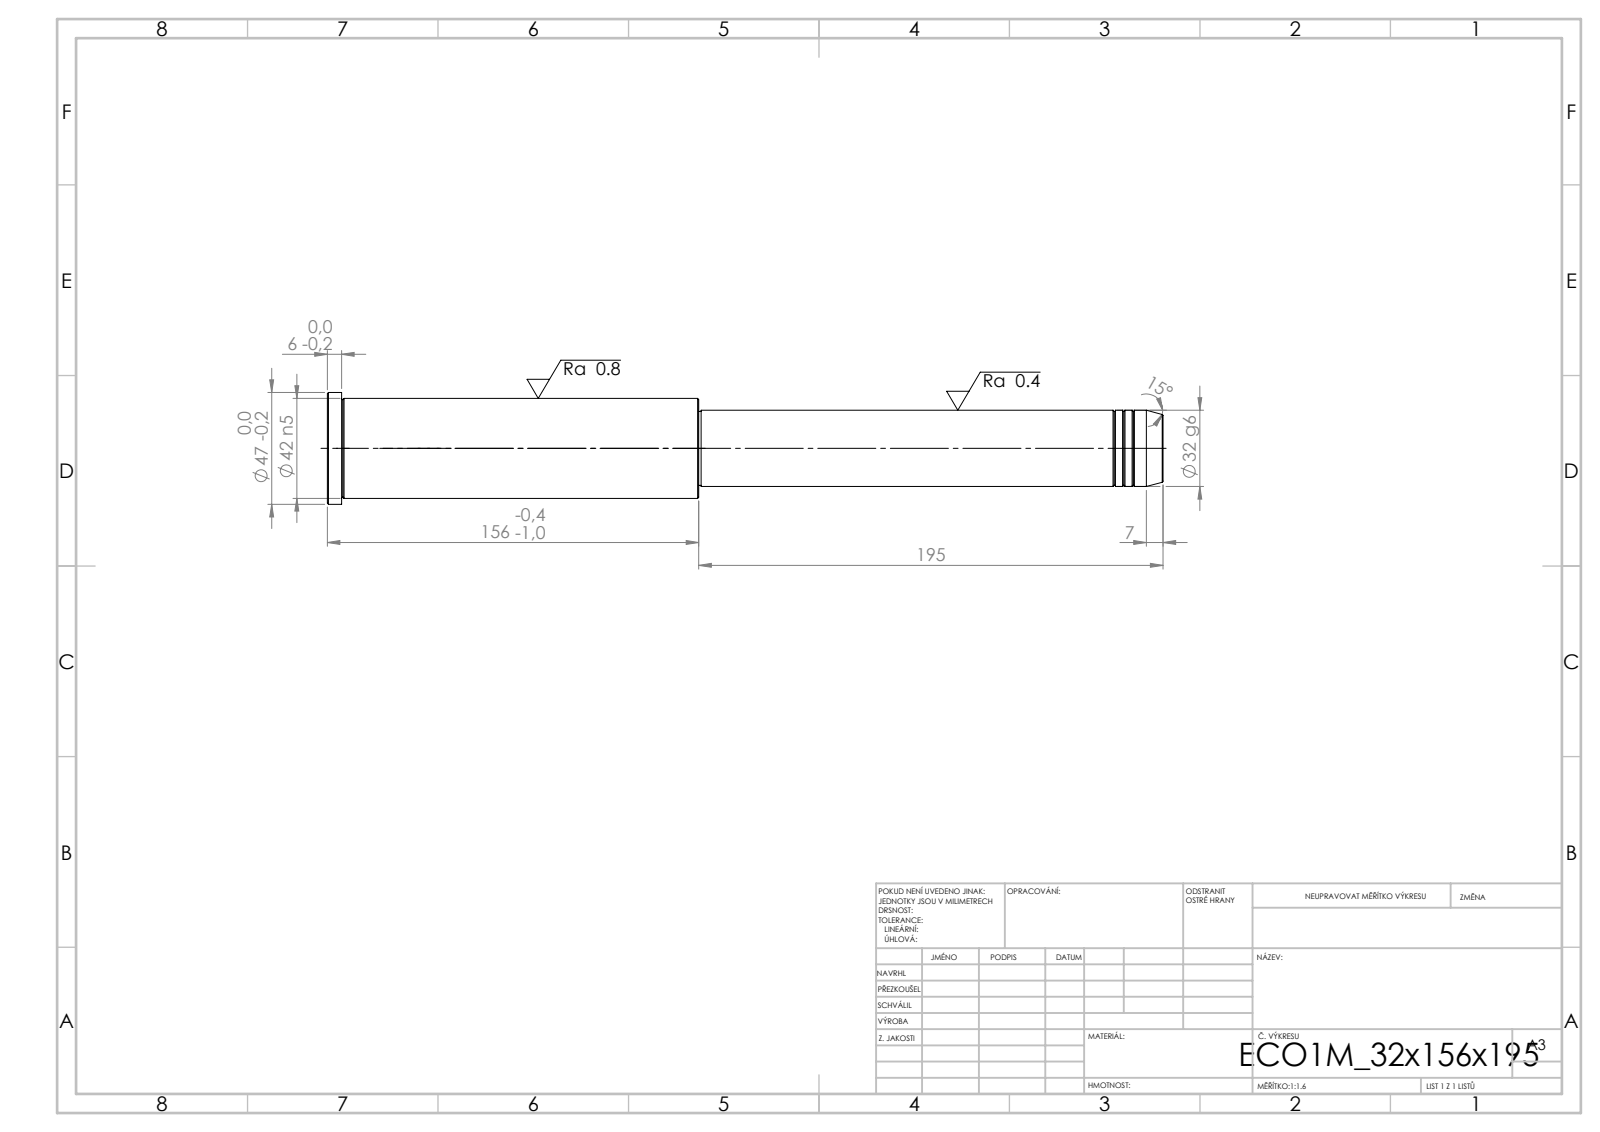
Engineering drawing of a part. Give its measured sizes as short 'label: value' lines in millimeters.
written by: SolidWorks 2019 (CONFIG_CONTROL_DESIGN)
unit: mm
bodies: 1 solid, 43 faces (5 planar, 14 cylindrical, 24 other)
size: 351 × 47 × 47
volume: 374 165 mm³; area: 43 794 mm²
bosses: 1× ⌀47, 1× ⌀42, 1× ⌀32, 1× ⌀31
face distances: 351, 195, 156, 345, 150, 6, 194, 1, 151, 157
